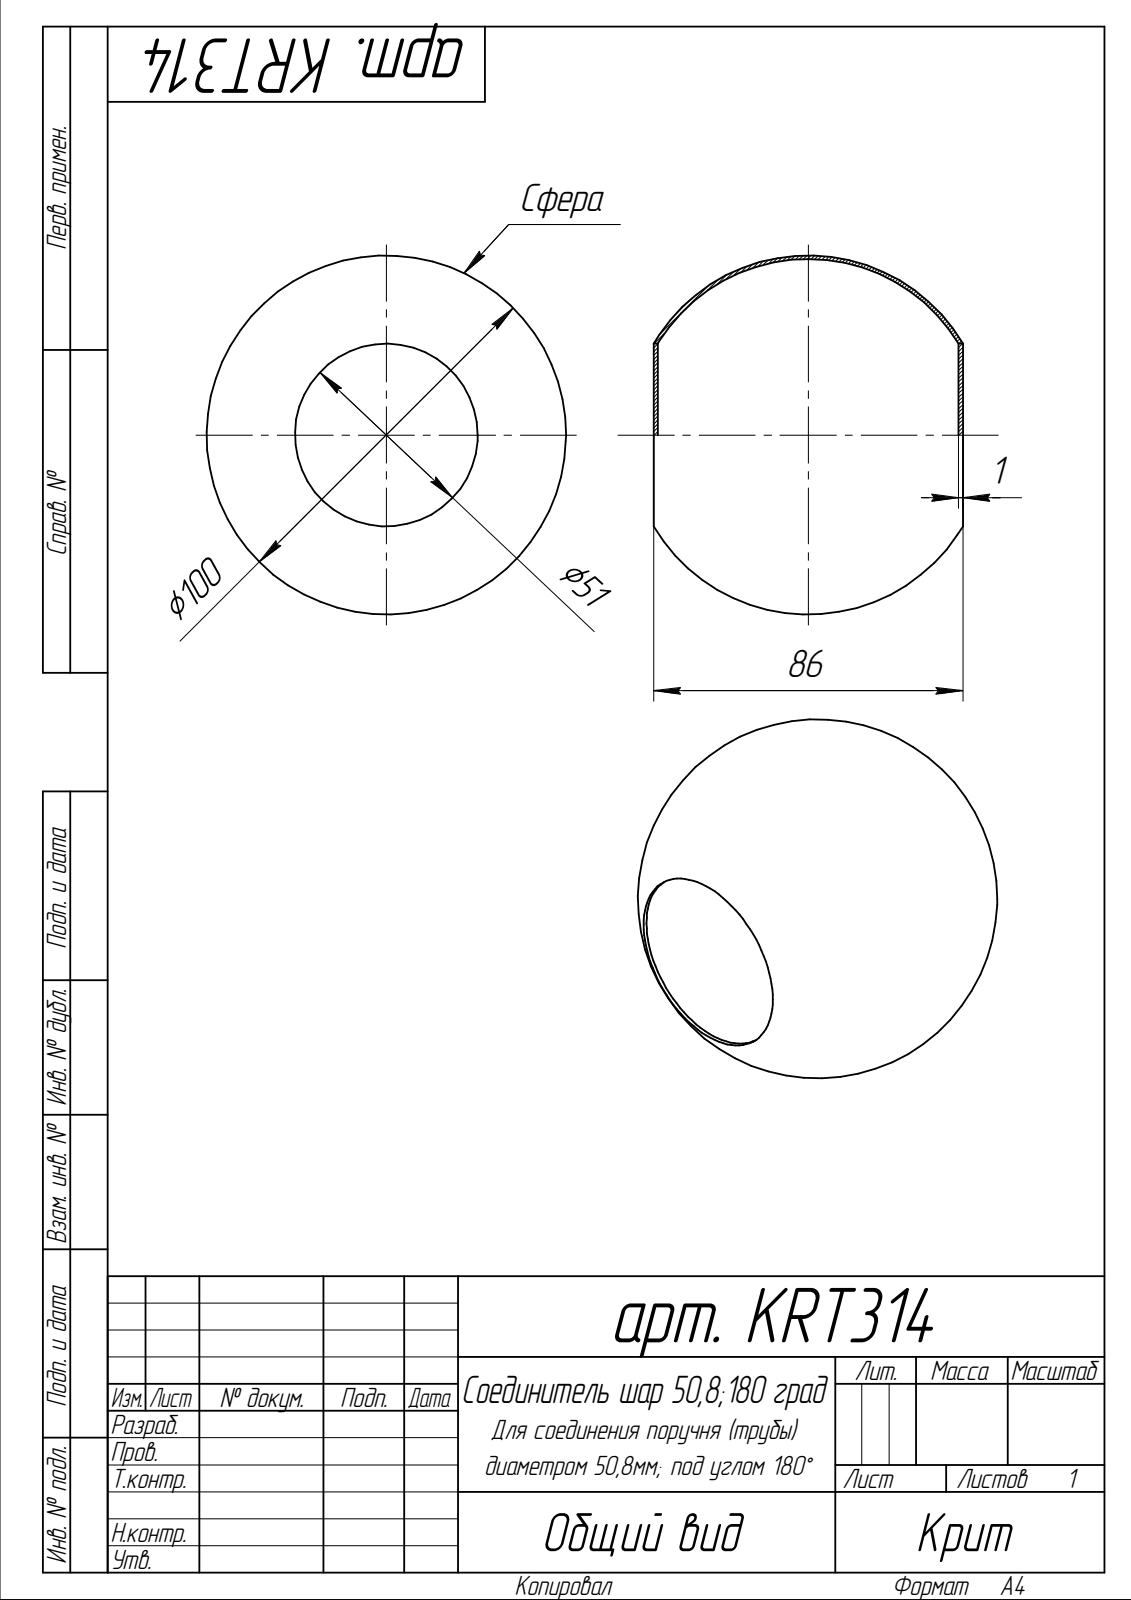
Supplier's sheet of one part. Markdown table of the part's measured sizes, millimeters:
| quantity | value |
| --- | --- |
| part name | арт. KRT314 |
| STEP written by | SolidWorks 2014 (AUTOMOTIVE_DESIGN) |
| units | millimeters |
| bodies | 1 solid, 8 faces (0 planar, 4 cylindrical, 4 other) |
| overall size | 100 × 100 × 86.08 |
| volume | 26 410 mm³ |
| surface area | 53 198 mm² |
| round holes (diameter × count) | 50.9 × 1 |
